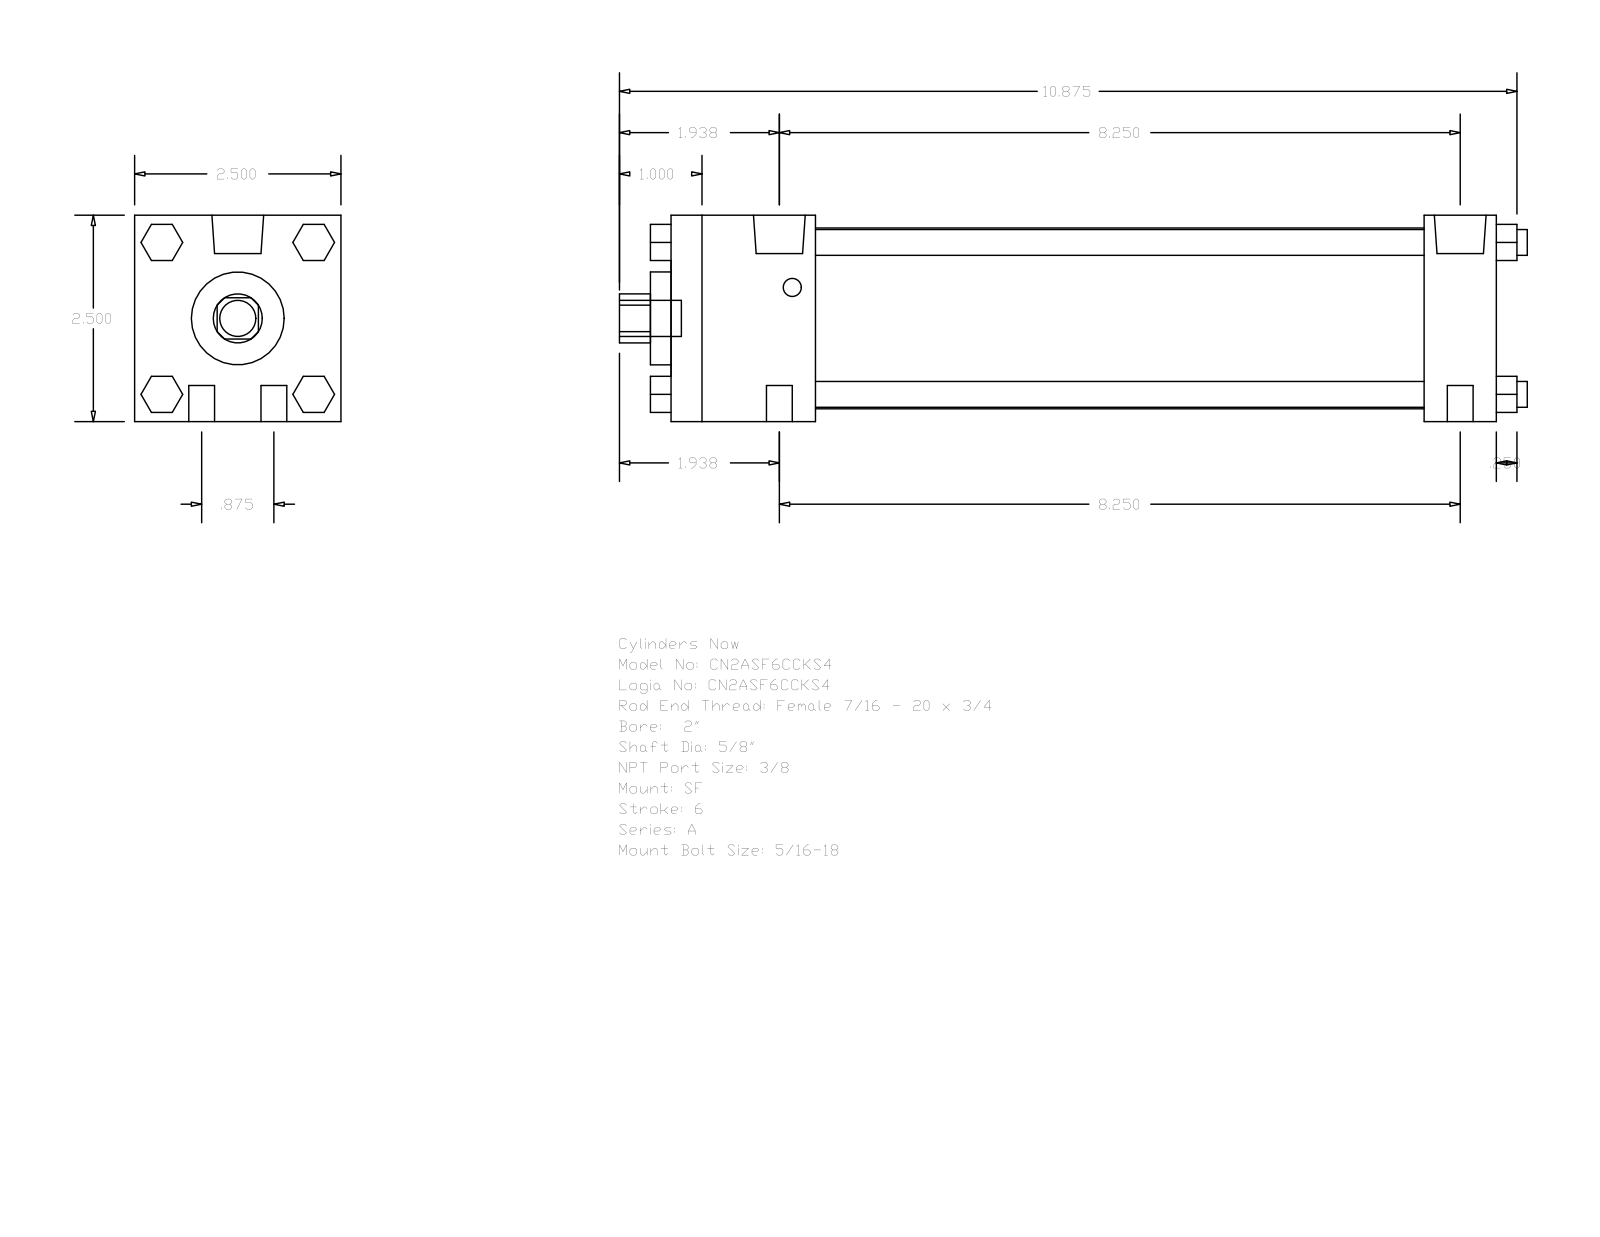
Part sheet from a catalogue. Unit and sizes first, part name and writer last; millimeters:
Units: millimetres
Overall size (bounding box): 279.4 × 63.5 × 63.5
Round holes (diameter × count): ⌀15.88 ×1, ⌀28.57 ×1, ⌀55.63 ×1
Round bosses / shafts (diameter × count): ⌀7.94 ×8, ⌀15.93 ×2, ⌀5.56 ×2, ⌀11.11 ×1
Partial cylindrical surfaces — rounded edges, fillets, slot ends (radius × count): R7.54 ×1
Main face-to-face distances: 63.5, 254, 231.77, 22.23, 44.45, 187.32, 209.55, 260.35, 6.35, 50.8
Bodies: 0 solids, 124 faces (94 planar, 30 cylindrical, 0 other)
Part name (STEP PRODUCT): A_SF__0200_0.625
STEP written by: GSSL Pune (CONFIG_CONTROL_DESIGN)
